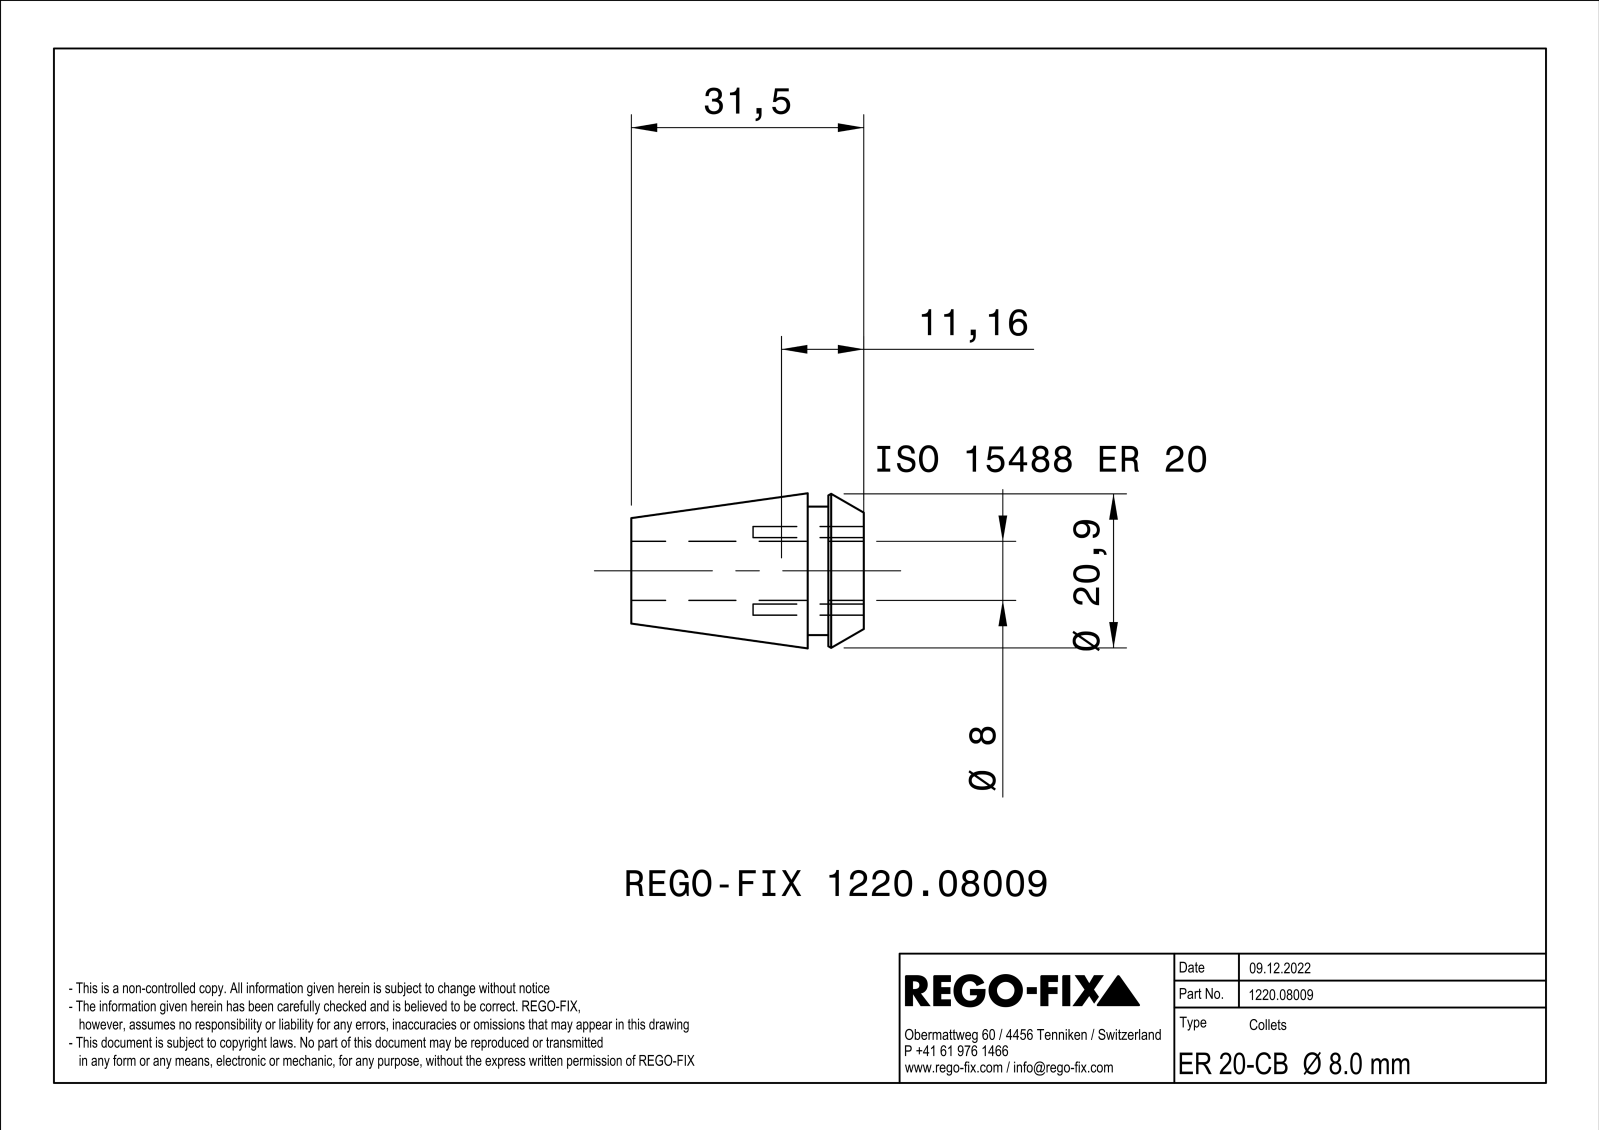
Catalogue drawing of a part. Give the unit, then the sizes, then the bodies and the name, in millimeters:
Units: millimetres
Overall size (bounding box): 31.5 × 20.99 × 20.99
Round holes (diameter × count): ⌀1.5 ×4, ⌀8 ×1
Round bosses / shafts (diameter × count): ⌀21 ×1, ⌀17.4 ×1
Main face-to-face distances: 0.6, 4.8, 31.5, 26.7, 7.6, 2.8, 23.9
Hole centre spacings: 5.25, 7.42, 10.5
Volume: 5 154 mm³ · Surface area: 6 274 mm²
Bodies: 1 solid, 178 faces (64 planar, 21 cylindrical, 93 other)
Part name (STEP PRODUCT): NOCUT
STEP written by: SIEMENS PLM Software Solid Edge ST10 (AUTOMOTIVE_DESIGN)
